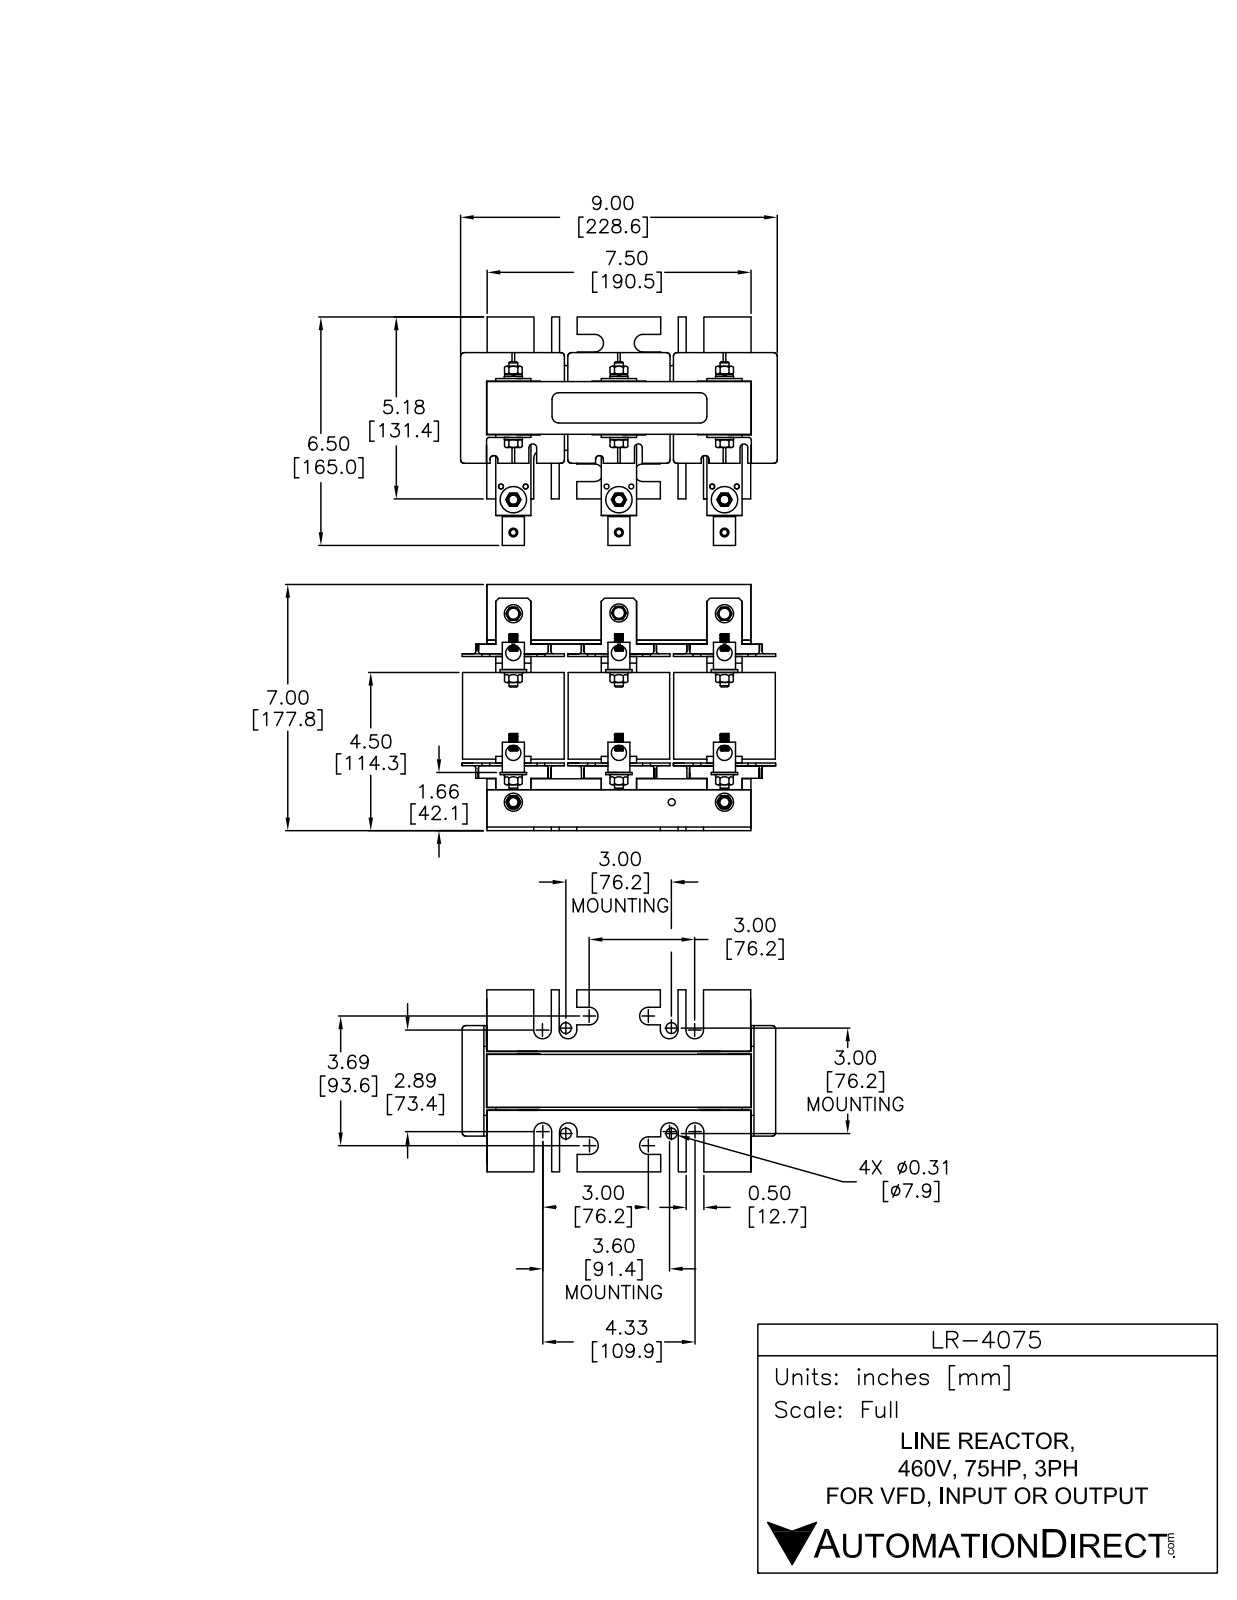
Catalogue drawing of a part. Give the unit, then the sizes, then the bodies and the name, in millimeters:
Units: millimetres
Overall size (bounding box): 227 × 177.7 × 160.75
Round holes (diameter × count): ⌀10.75 ×6, ⌀11.5 ×3, ⌀11.51 ×3
Round bosses / shafts (diameter × count): ⌀15 ×11, ⌀18.75 ×9, ⌀6 ×9, ⌀10.5 ×6, ⌀6 ×2
Partial cylindrical surfaces — rounded edges, fillets, slot ends (radius × count): R15 ×16, R6.35 ×12, R7 ×12, R2.75 ×6, R15.25 ×6, R1.5 ×4, R23.44 ×3, R24 ×3
Main face-to-face distances: 76.5, 2, 9, 87.5, 85.5, 7, 78.5, 38, 38.5, 42.5
Hole centre spacings: 76.5, 76.84, 104.71, 153, 7.17, 71.5, 153.17, 168.88
Volume: 2 667 000 mm³ · Surface area: 555 030 mm²
Bodies: 47 solids, 972 faces (716 planar, 244 cylindrical, 12 other)
Part name (STEP PRODUCT): LR-4075
STEP written by: SolidWorks 2011 (AUTOMOTIVE_DESIGN)
